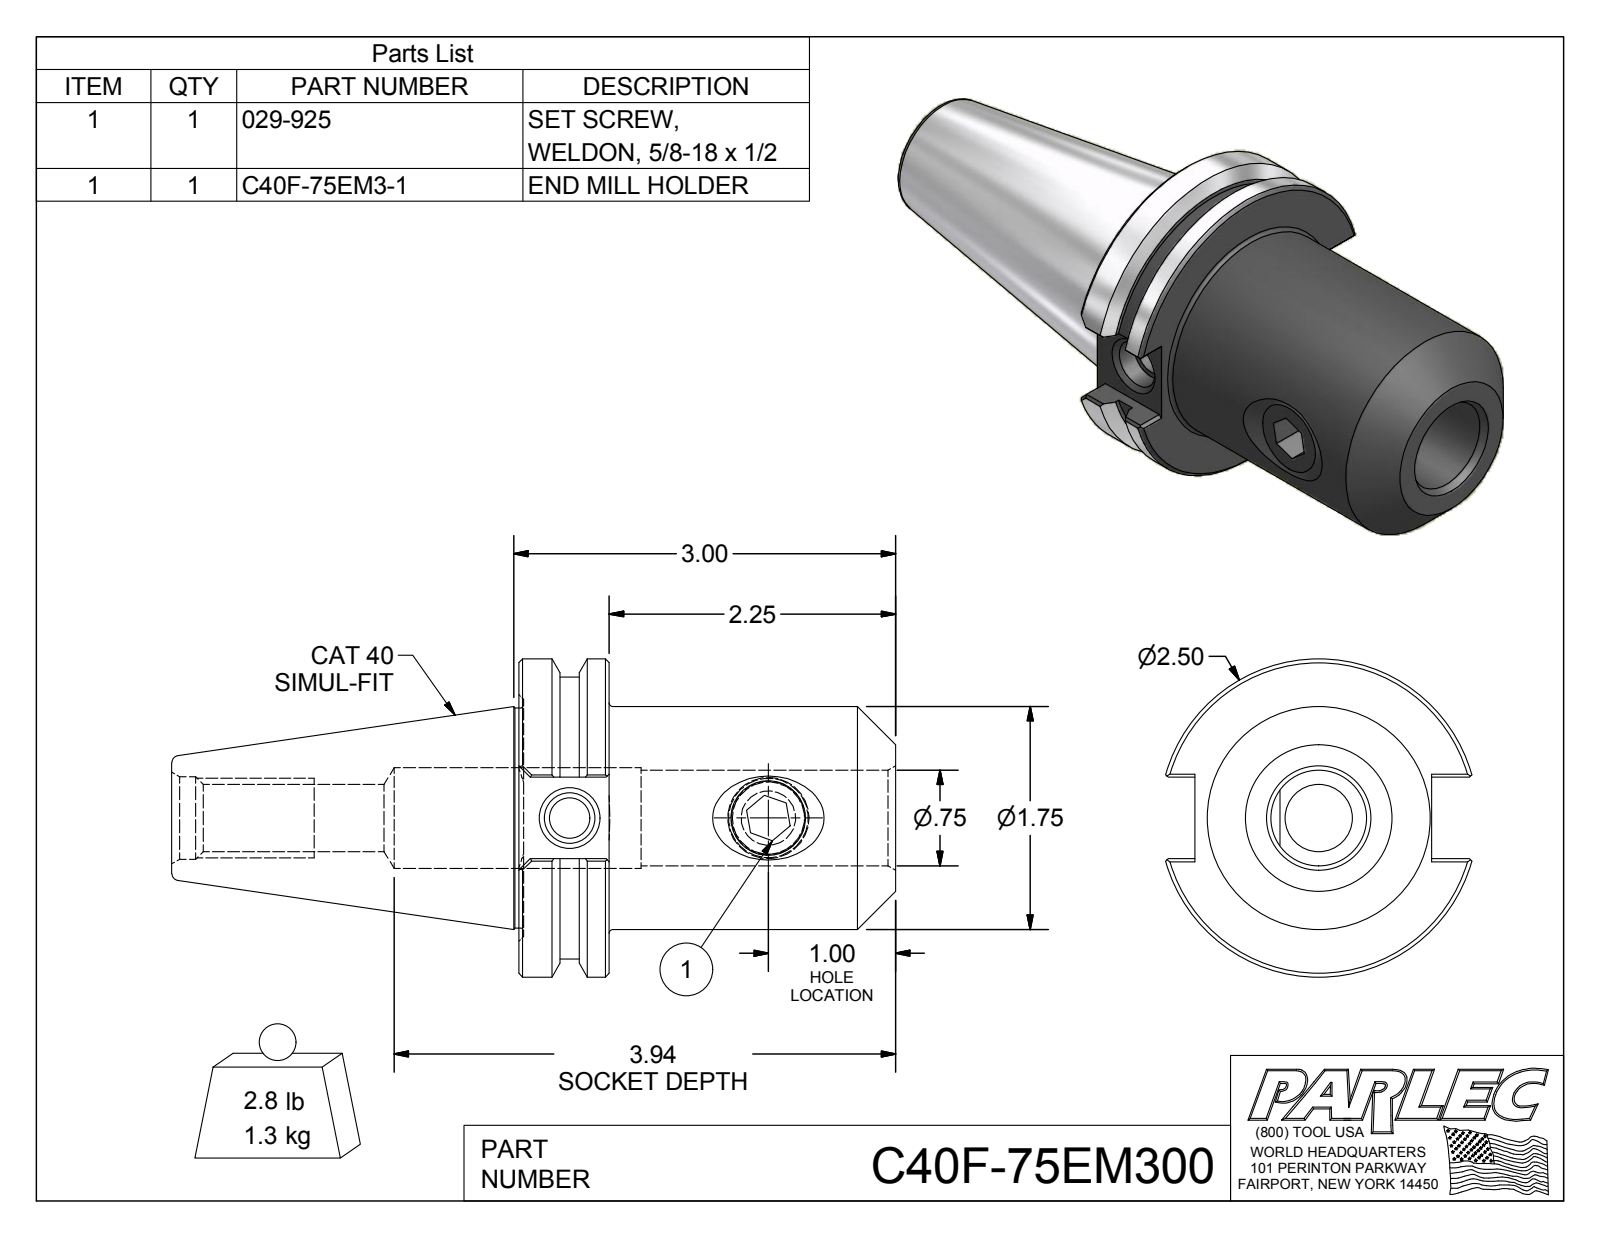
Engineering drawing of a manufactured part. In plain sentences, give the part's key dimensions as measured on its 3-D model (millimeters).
The part is named "C40F-75EM300; C40F-75EM3-1; 029-925". Its 3-D file was written by "Autodesk Inventor 2012 (AUTOMOTIVE_DESIGN)". It is 2 solids with 101 faces: 41 planar, 29 cylindrical and 31 other. Overall it measures 144.4 by 63.5 by 61.1 millimeters. Its volume is 159 800 cubic millimeters and its surface area 33 440 square millimeters. Round holes: 1 of diameter 8, 1 of diameter 10.1, 1 of diameter 13.4, 1 of diameter 14.7, 1 of diameter 16.5, 1 of diameter 19.1, 1 of diameter 20.1. Round bosses or shafts: 1 of diameter 63.5, 1 of diameter 56.4, 1 of diameter 44.5, 1 of diameter 43.9, 1 of diameter 15.9. Partial cylindrical surfaces (rounded edges, fillets, slot ends): 12 of radius 0.5. The main face-to-face distances are 15.9, 73, 57.2, 16.3, 8, 47.2, 71.4, 87.3, 144.4, 43. The hole center spacings are 39.6.
